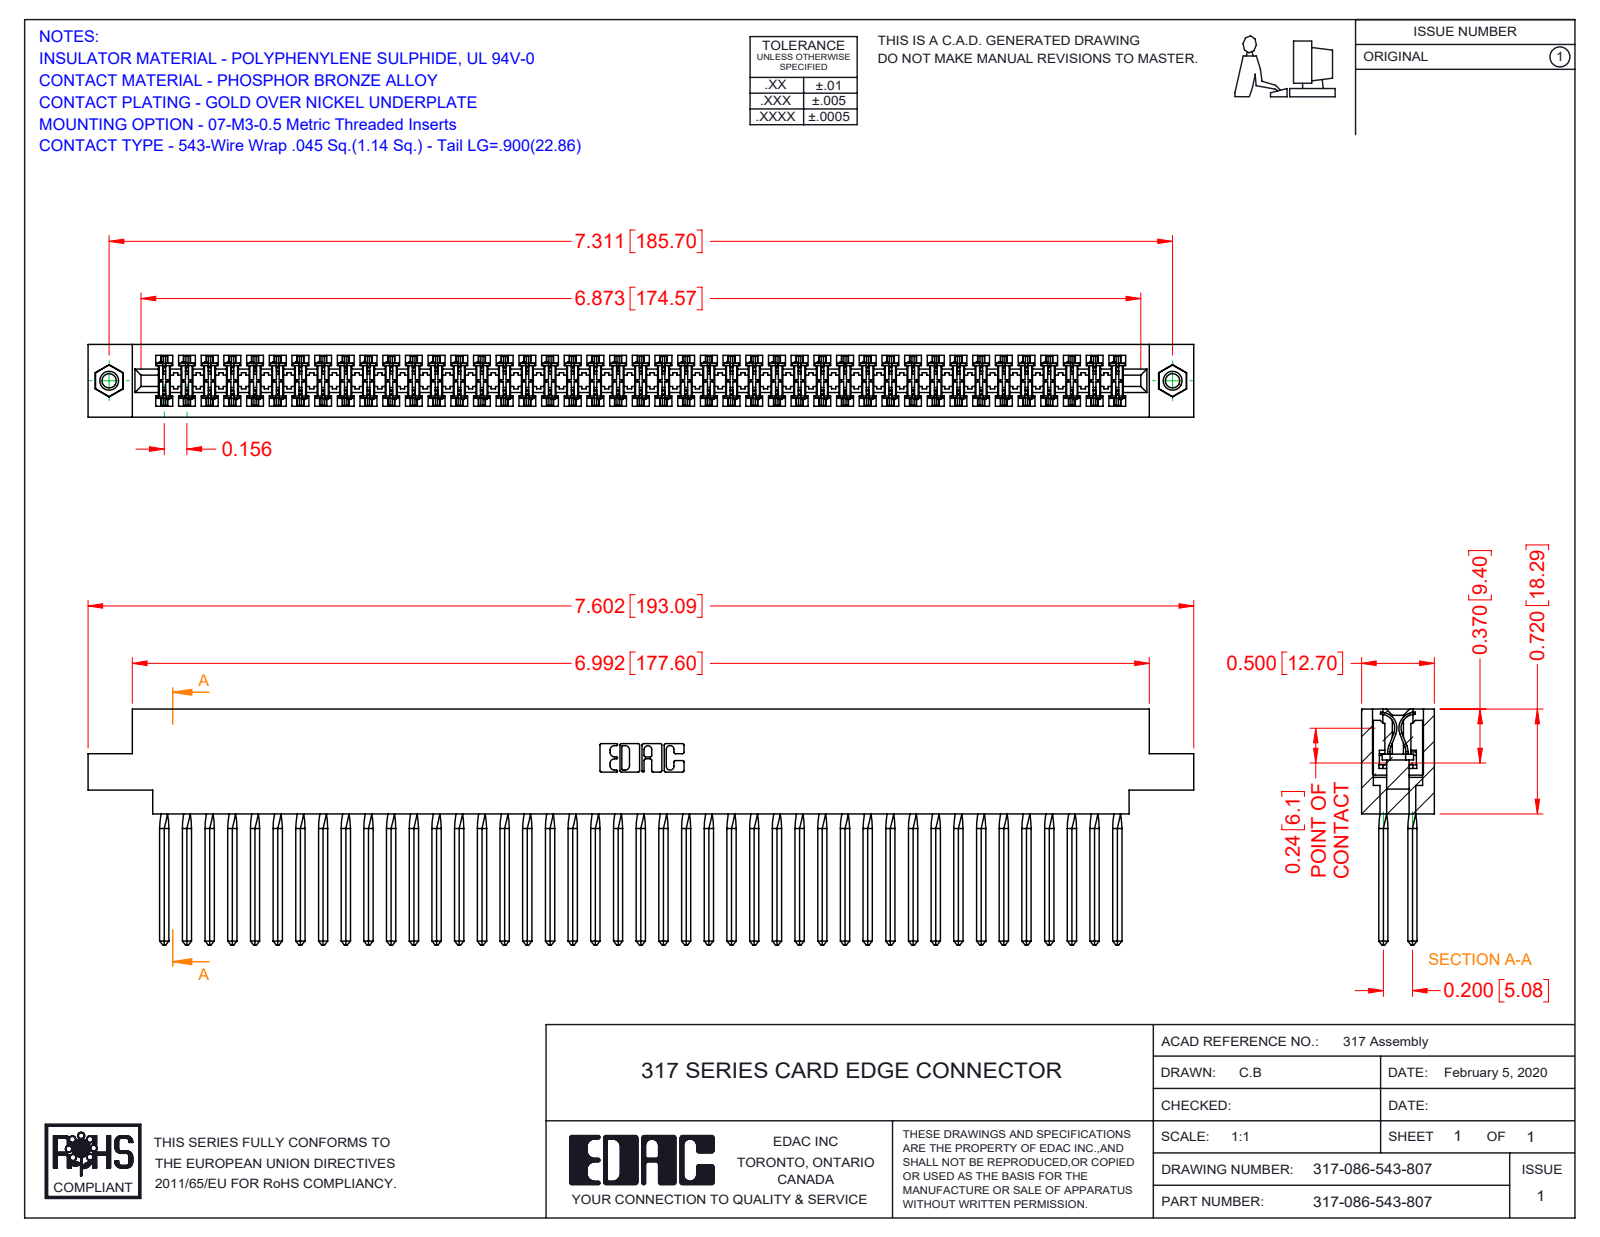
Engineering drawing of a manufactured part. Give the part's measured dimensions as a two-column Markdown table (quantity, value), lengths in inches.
| quantity | value |
| --- | --- |
| part name | 345-250-001_345-250-005-103; 317-086-543-807; 317 Part_.156 Dia - TI; 317-290-001_543 |
| STEP written by | SolidWorks 2016 (CONFIG_CONTROL_DESIGN) |
| units | inches |
| bodies | 89 solids, 7816 faces (6368 planar, 1088 cylindrical, 360 other) |
| overall size | 7.602 × 1.62 × 0.5 |
| volume | 2.005 in³ |
| surface area | 77.37 in² |
| round holes (diameter × count) | 0.098 × 2, 0.125 × 2, 0.156 × 2 |
| round bosses / shafts (diameter × count) | 0.155 × 2 |
| partial cylindrical surfaces (radius × count) | 0.015 × 172, 0.01 × 22, 0.007 × 6, 0.031 × 6, 0.026 × 3, 0.095 × 2, 0.1 × 2, 0.11 × 2 |
| main face-to-face distances | 0.5, 0.075, 0.425, 0.35, 0.195, 0.11, 0.094, 0.2, 0.115, 0.131 |
| hole center spacings | 7.311 |
